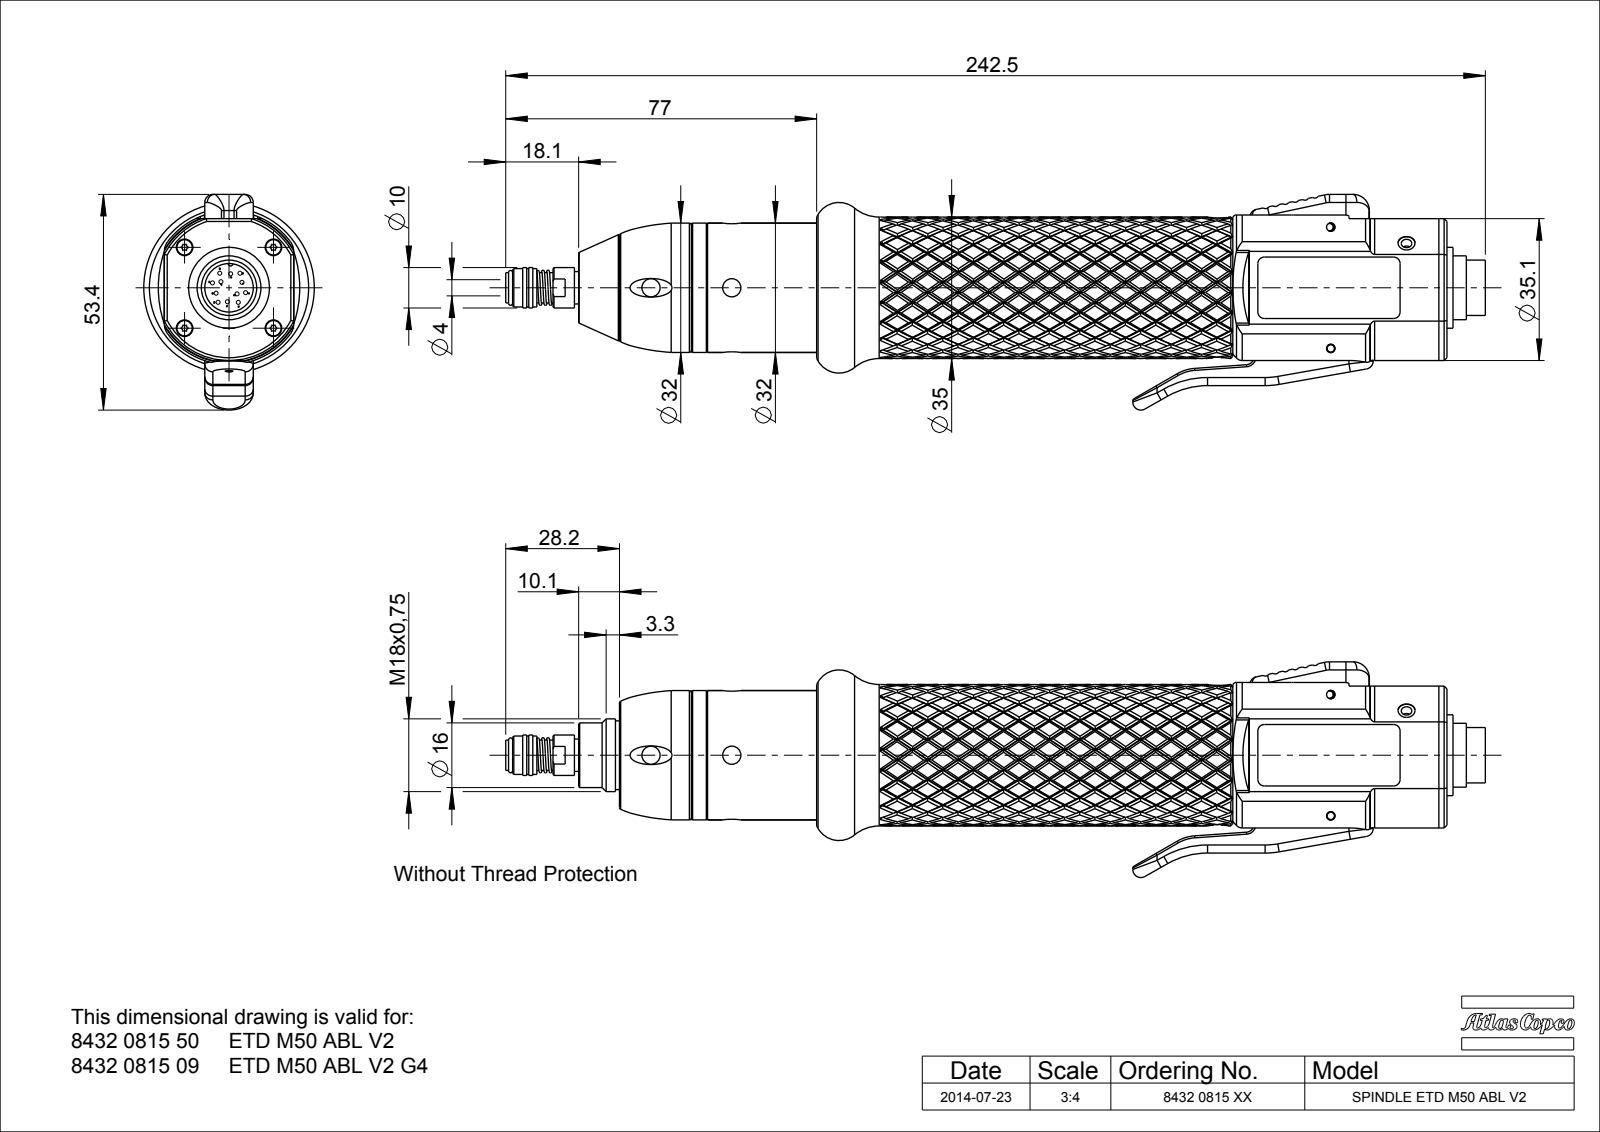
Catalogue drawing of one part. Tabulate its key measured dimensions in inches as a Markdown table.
| quantity | value |
| --- | --- |
| part name | 4216115101; 4216258506; 4216258505; 4216263700 (+8 more) |
| STEP written by | PRO/ENGINEER BY PARAMETRIC TECHNOLOGY CORPORATION, 2013410 (CONFIG_CONTROL_DESIGN) |
| units | inches |
| bodies | 26 solids, 3757 faces (854 planar, 985 cylindrical, 1918 other) |
| overall size | 9.545 × 2.101 × 1.661 |
| volume | 4.87 in³ |
| surface area | 137.9 in² |
| round holes (diameter × count) | 0.079 × 12, 0.177 × 6, 0.063 × 5, 0.091 × 4, 0.157 × 4, 0.083 × 3, 0.165 × 3, 0.102 × 2, 0.13 × 2, 0.059 × 1, 0.071 × 1, 0.118 × 1 |
| round bosses / shafts (diameter × count) | 0.039 × 12, 0.15 × 4, 1.378 × 1, 1.26 × 1, 1.102 × 1, 1.063 × 1, 1.043 × 1, 0.827 × 1 |
| partial cylindrical surfaces (radius × count) | 0.004 × 24, 0.021 × 24, 0.079 × 19, 0.039 × 10, 0.008 × 9, 0.02 × 8, 0.236 × 8, 0.177 × 6 |
| main face-to-face distances | 0.079, 0.858, 0.394, 1.244, 1.252, 8.063, 7.984, 2.087, 2.008, 5.976 |
| hole center spacings | 0.787, 0.585, 0.474, 0.866, 1.072, 1.17, 5.867, 6.055 |
